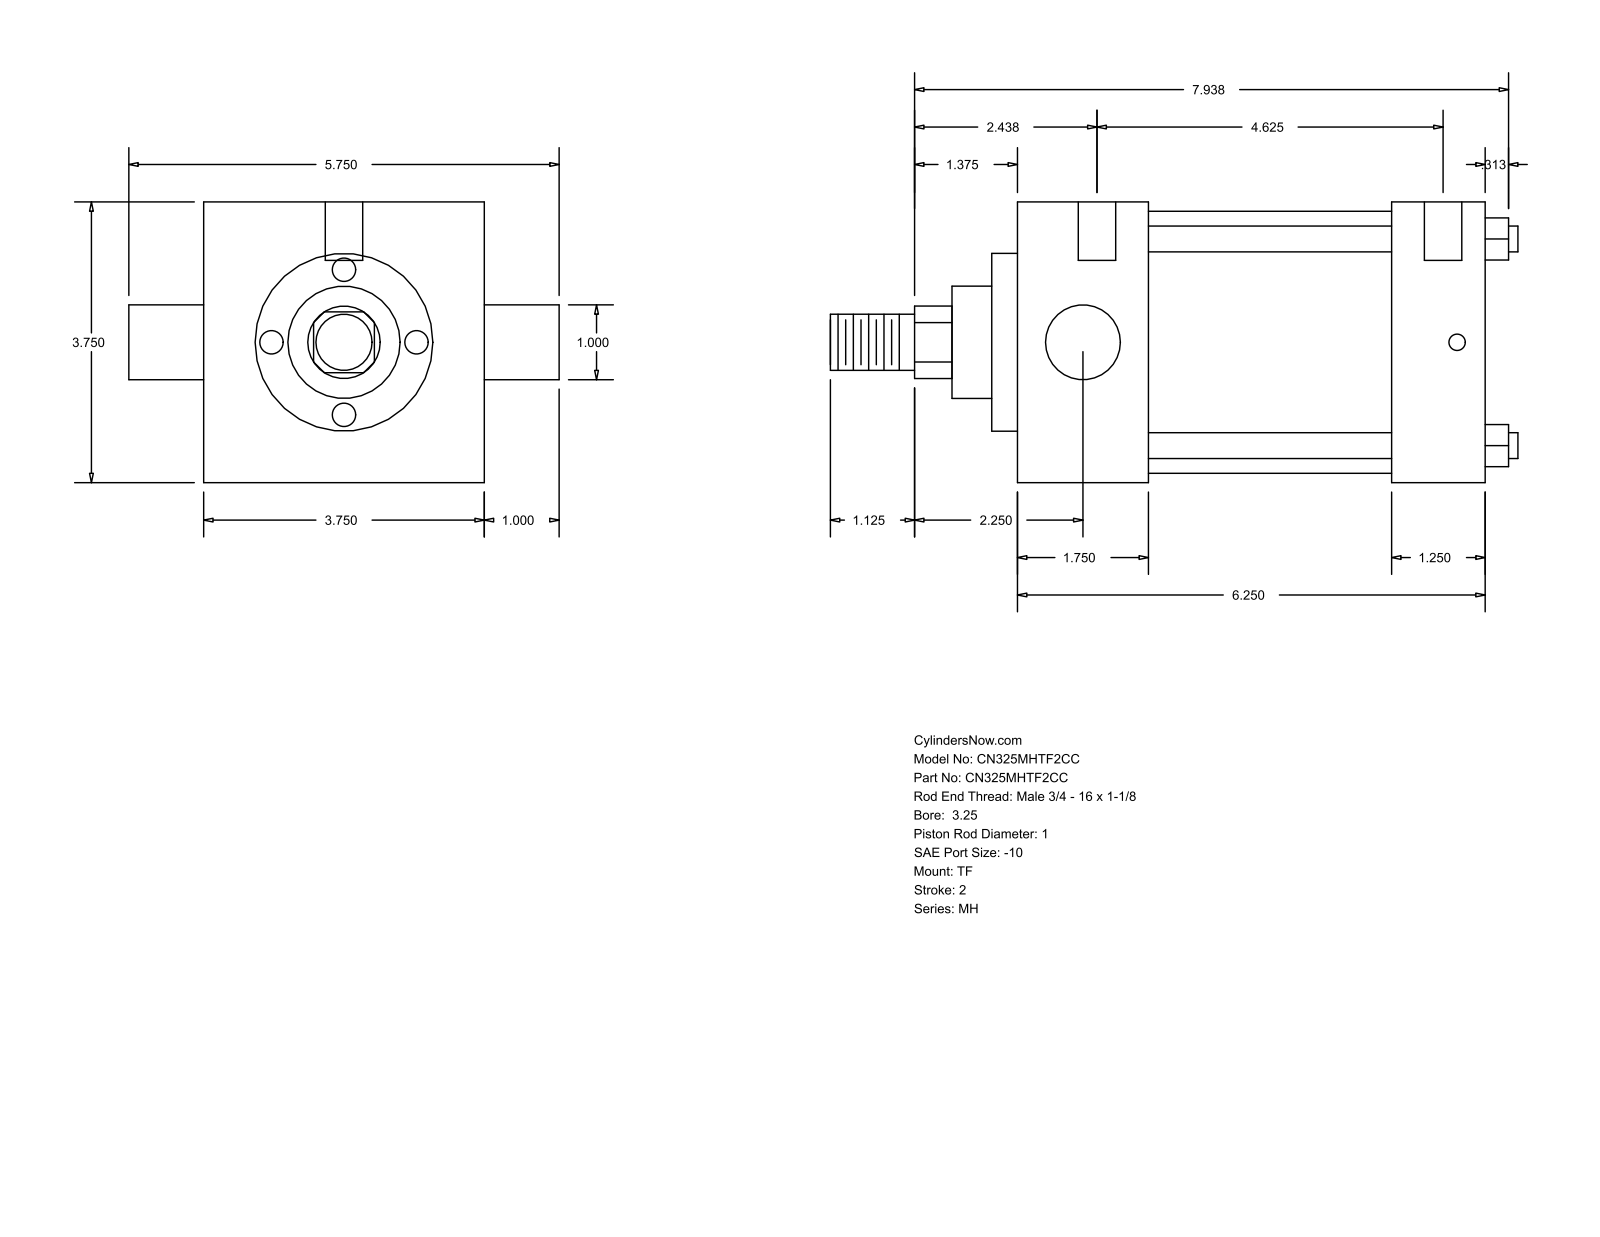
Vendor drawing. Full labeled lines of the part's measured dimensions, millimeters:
Part name (STEP PRODUCT): MH_TF__0325_1
STEP written by: GSSL Pune (CONFIG_CONTROL_DESIGN)
Units: millimetres
Bodies: 0 solids, 86 faces (61 planar, 25 cylindrical, 0 other)
Overall size (bounding box): 233.36 × 146.05 × 95.25
Round holes (diameter × count): ⌀5.56 ×3, ⌀12.7 ×2
Round bosses / shafts (diameter × count): ⌀8.76 ×4, ⌀25.4 ×2, ⌀88.9 ×1, ⌀60.33 ×1, ⌀38.1 ×1, ⌀19.05 ×1
Partial cylindrical surfaces — rounded edges, fillets, slot ends (radius × count): R12.29 ×1
Main face-to-face distances: 95.24, 158.76, 44.46, 127.01, 82.55, 114.3, 31.75, 8.73, 53.19, 135.74
Hole centre spacings: 1.58, 4.76, 117.48, 119.06, 122.24, 123.82
